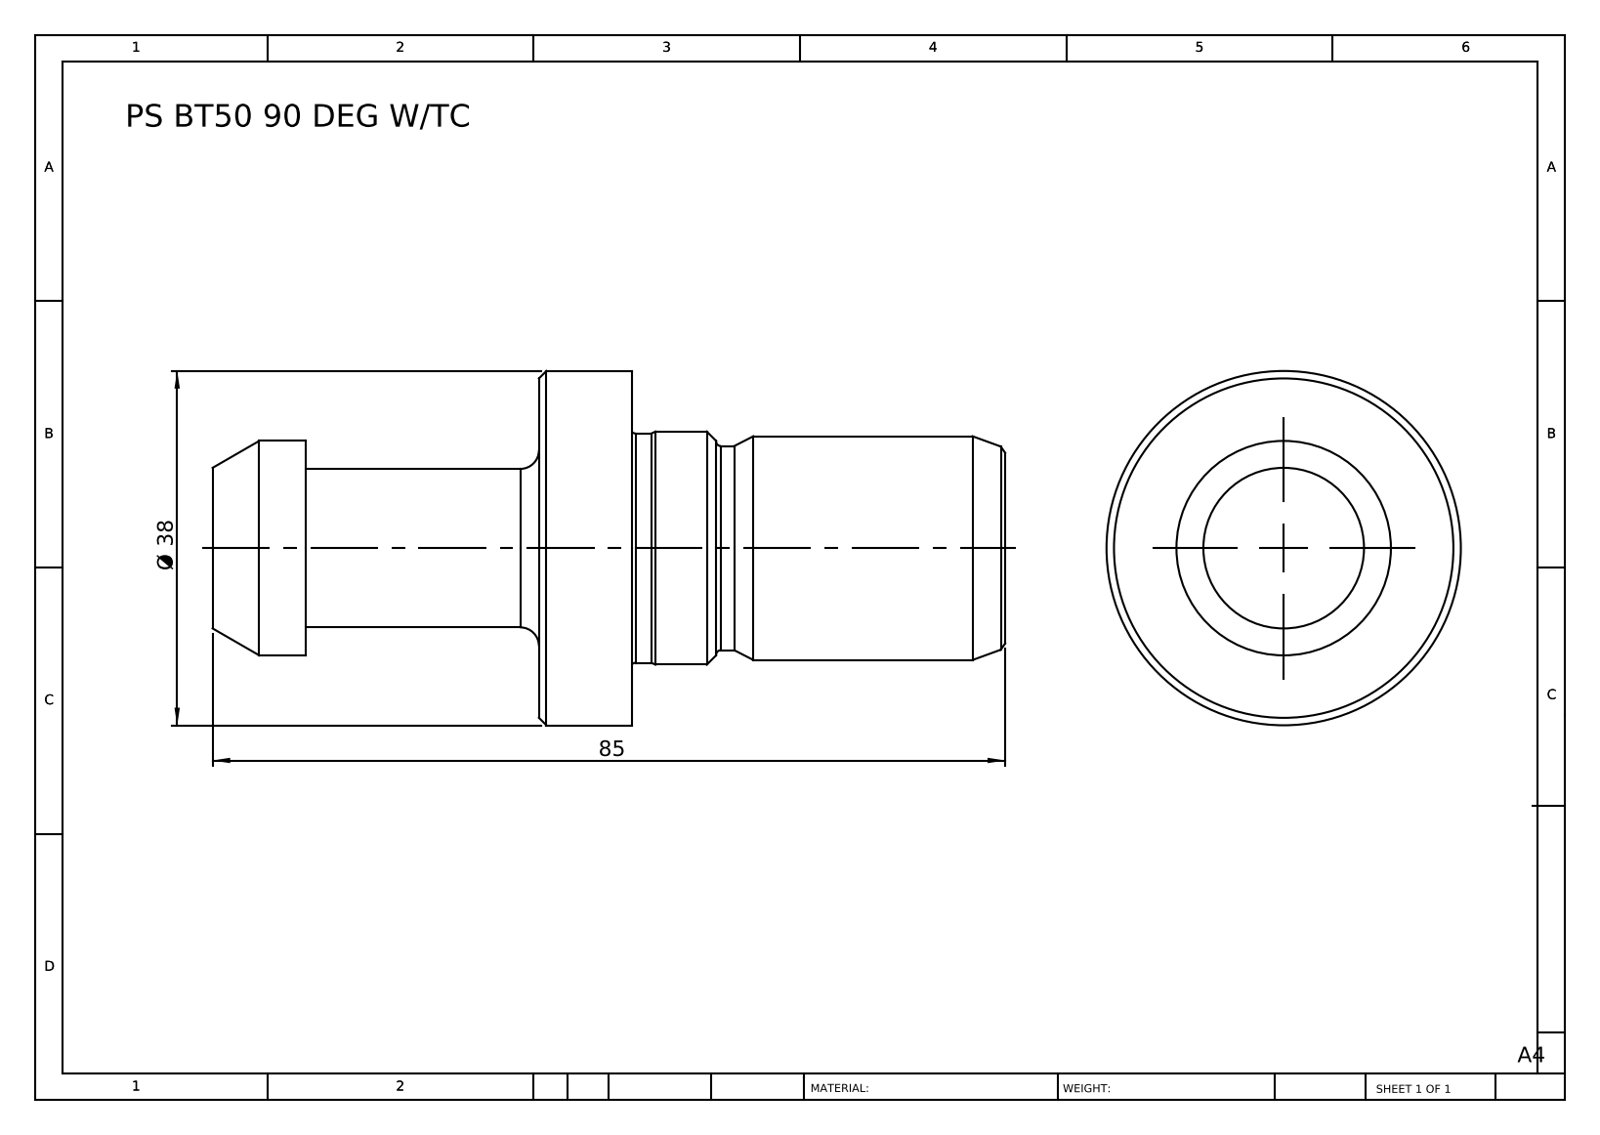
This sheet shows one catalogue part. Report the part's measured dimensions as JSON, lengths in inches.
{"part_name": "PS BT50 90 DEG W-TC", "step_written_by": "SolidWorks 2014 (CONFIG_CONTROL_DESIGN)", "units": "inches", "bodies": {"solids": 1, "faces": 42, "planar": 6, "cylindrical": 14, "other": 22}, "overall_size": [3.346, 1.496, 1.496], "volume_in3": 2.36, "surface_area_in2": 13.31, "round_bosses_or_shafts": [[1.496, 1], [0.984, 1], [0.969, 1], [0.945, 1], [0.906, 1], [0.862, 1], [0.669, 1]], "face_to_face_distances": [0.394, 1.378, 1.575, 1.969, 3.346, 1.772, 2.953, 0.984, 1.22, 0.354]}
